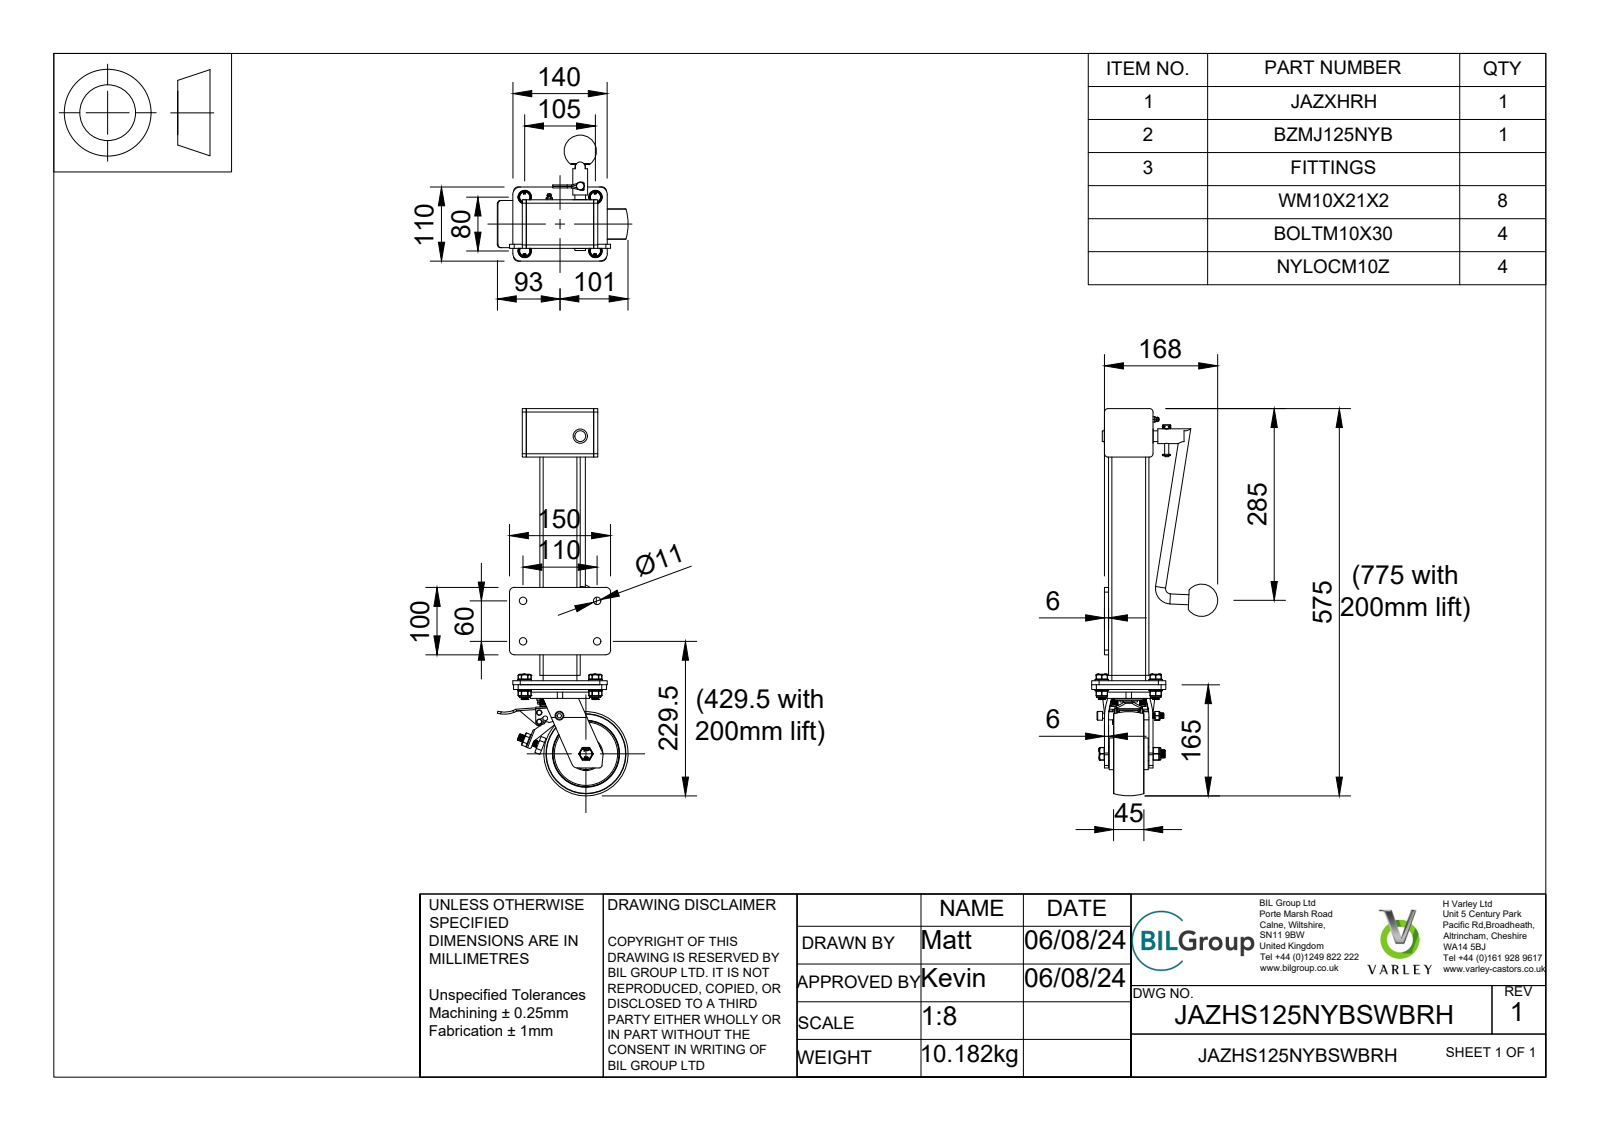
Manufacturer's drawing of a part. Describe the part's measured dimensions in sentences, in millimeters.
The part is named "JAZHS125NYBSWBRH v3; BZMJ125ASSWB - 60 v1; FABRICATED STEEL TOP PLATE (1); FABRICATED STEEL TOP PLATE Geometry (1) (+8 more)". Its 3-D file was written by "Autodesk Translation Framework v13.14.0.145 (AUTOMOTIVE_DESIGN)". It is 74 solids with 1785 faces: 727 planar, 752 cylindrical and 306 other. Overall it measures 575 by 194 by 187.03 millimeters. Its volume is 2 199 000 cubic millimeters and its surface area 637 987 square millimeters. Round holes: 5 of diameter 10, 5 of diameter 12, 4 of diameter 10.5, 4 of diameter 11, 3 of diameter 6, 2 of diameter 16, 1 of diameter 3, 1 of diameter 6.25, 1 of diameter 6.75, 1 of diameter 7, 1 of diameter 8, 1 of diameter 12.5. Round bosses or shafts: 10 of diameter 2, 8 of diameter 7.5, 4 of diameter 20, 4 of diameter 16, 4 of diameter 9.85, 4 of diameter 8.14, 4 of diameter 8, 2 of diameter 12. Partial cylindrical surfaces (rounded edges, fillets, slot ends): 104 of radius 0.5, 17 of radius 5, 16 of radius 0.33, 16 of radius 0.64, 16 of radius 1, 8 of radius 0.63, 8 of radius 0.64, 8 of radius 4.84. The main face-to-face distances are 3.5, 1.5, 6, 55, 51.5, 5, 56.5, 62.5, 60, 50. The hole center spacings are 66, 60, 80, 105, 110, 125.3, 132, 13.65.
